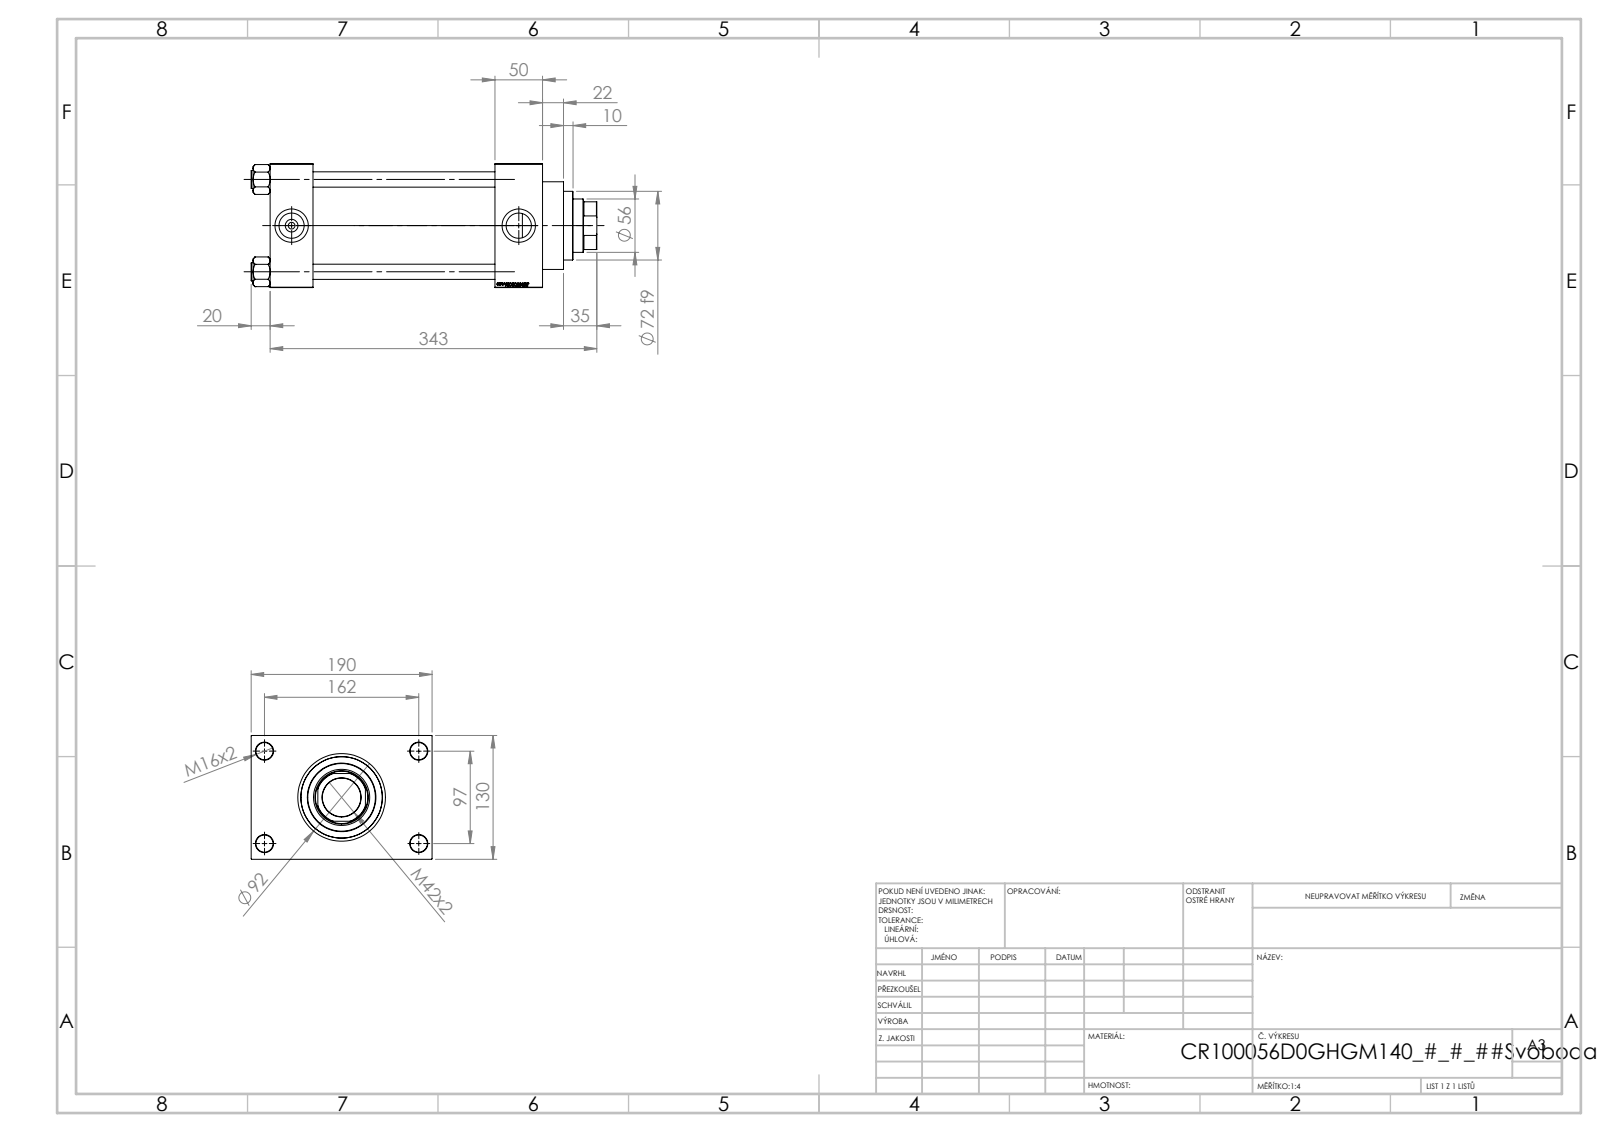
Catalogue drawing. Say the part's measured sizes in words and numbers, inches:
The part is named "V215_VC_A; NUT_M5_D; V215CR_VCP_D; V215CR_D_Body (+1 more)". Its 3-D file was written by "SolidWorks 2019 (CONFIG_CONTROL_DESIGN)". It is 11 solids with 1151 faces: 545 planar, 88 cylindrical and 518 other. Overall it measures 14.291 by 7.48 by 5.118 inches. Its volume is 191.4 cubic inches and its surface area 752.2 square inches. Round holes: 4 of diameter 0.63, 4 of diameter 0.709, 2 of diameter 0.276, 2 of diameter 1.041, 2 of diameter 1.378, 1 of diameter 1.594, 1 of diameter 2.205, 1 of diameter 2.323, 1 of diameter 2.992, 1 of diameter 3.366, 1 of diameter 3.937. Round bosses or shafts: 4 of diameter 0.748, 1 of diameter 4.173, 1 of diameter 3.622, 1 of diameter 2.835. Partial cylindrical surfaces (rounded edges, fillets, slot ends): 1 of radius 1.063. The main face-to-face distances are 5.118, 1.969, 1.772, 9.291, 7.52, 11.26, 9.488, 1.181, 7.48, 6.299. The hole center spacings are 1.281, 2.698, 3.717, 3.815, 4.026, 5.096, 6.367, 3.819.
